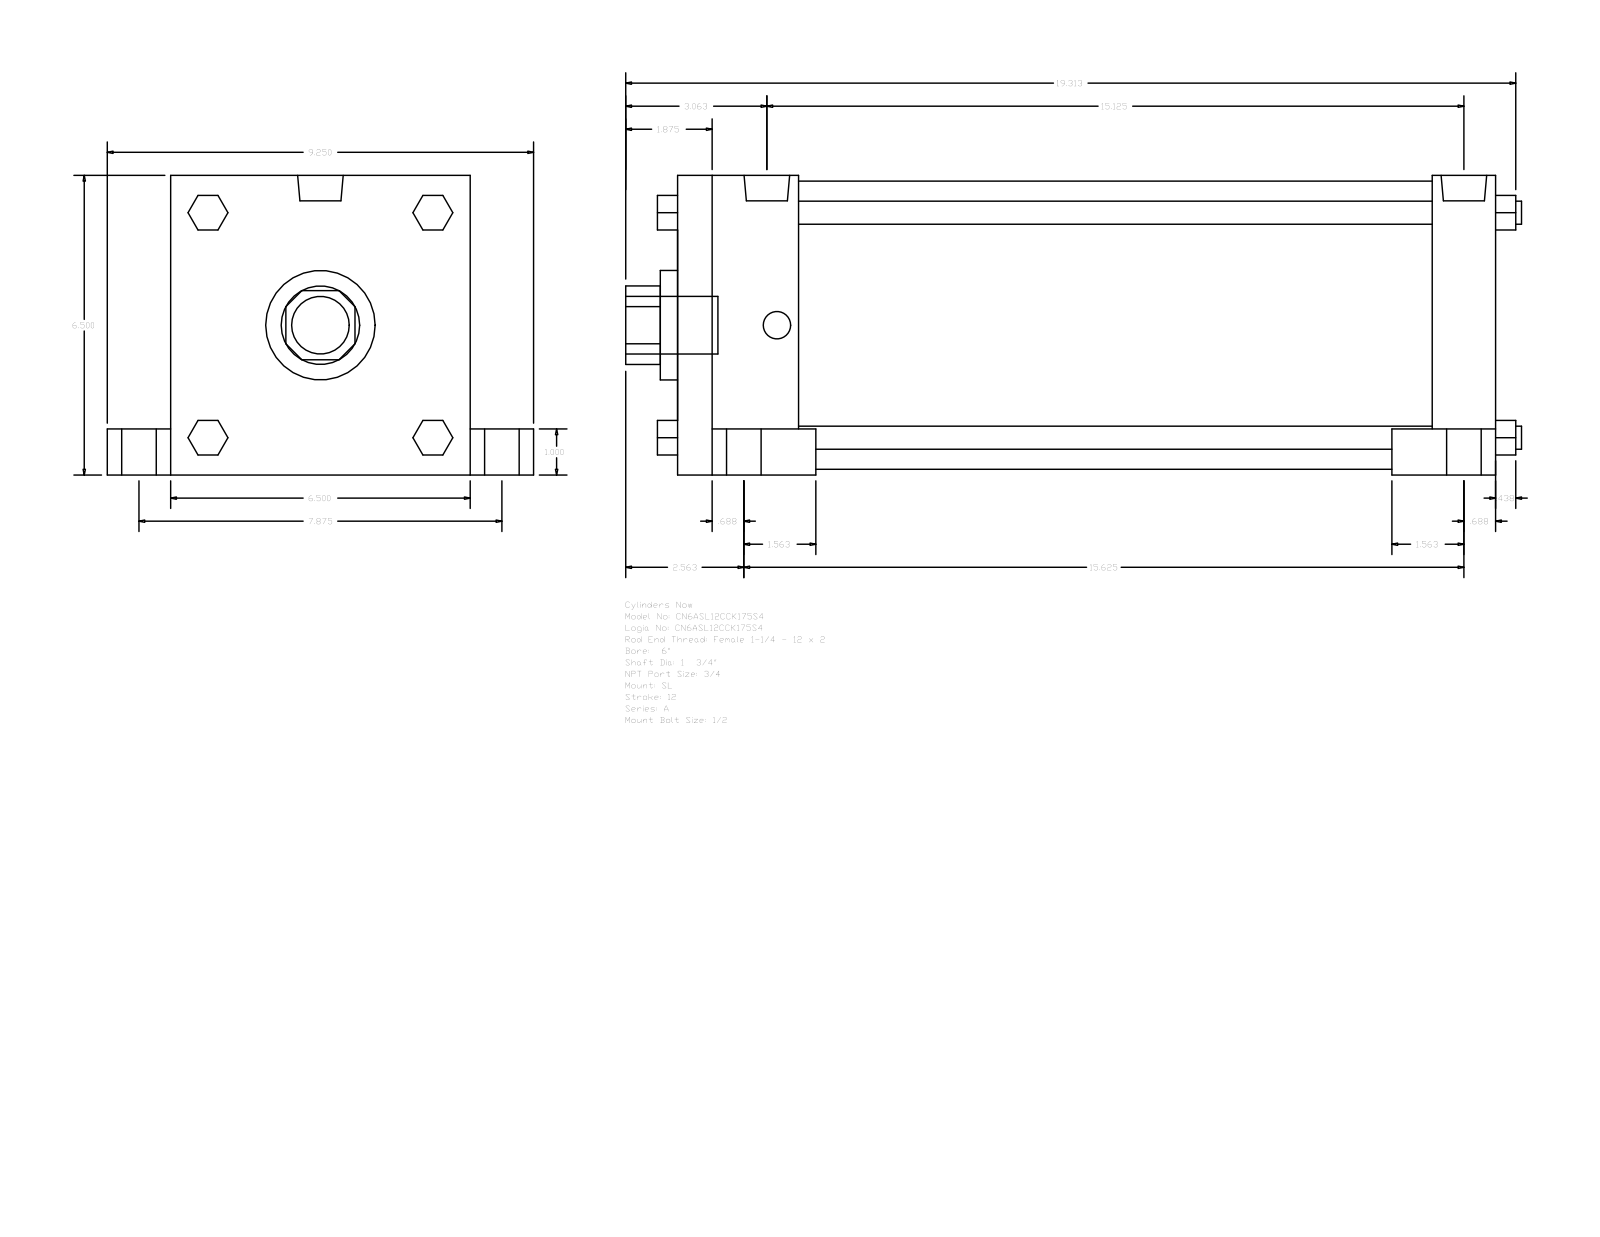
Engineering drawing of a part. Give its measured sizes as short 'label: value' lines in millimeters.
name: A_SL__0600_1.75
written by: GSSL Pune (CONFIG_CONTROL_DESIGN)
unit: mm
bodies: 0 solids, 150 faces (114 planar, 36 cylindrical, 0 other)
size: 493.71 × 234.95 × 165.1
holes: 1× ⌀44.45, 1× ⌀60.33, 1× ⌀158.75
bosses: 4× ⌀25.4, 4× ⌀19.05, 4× ⌀15.08, 4× ⌀12.7, 2× ⌀25.12, 1× ⌀31.75
rounds: 1× R21.63
face distances: 165.1, 450.86, 66.68, 384.18, 415.93, 349.25, 34.93, 34.92, 25.4, 139.7
